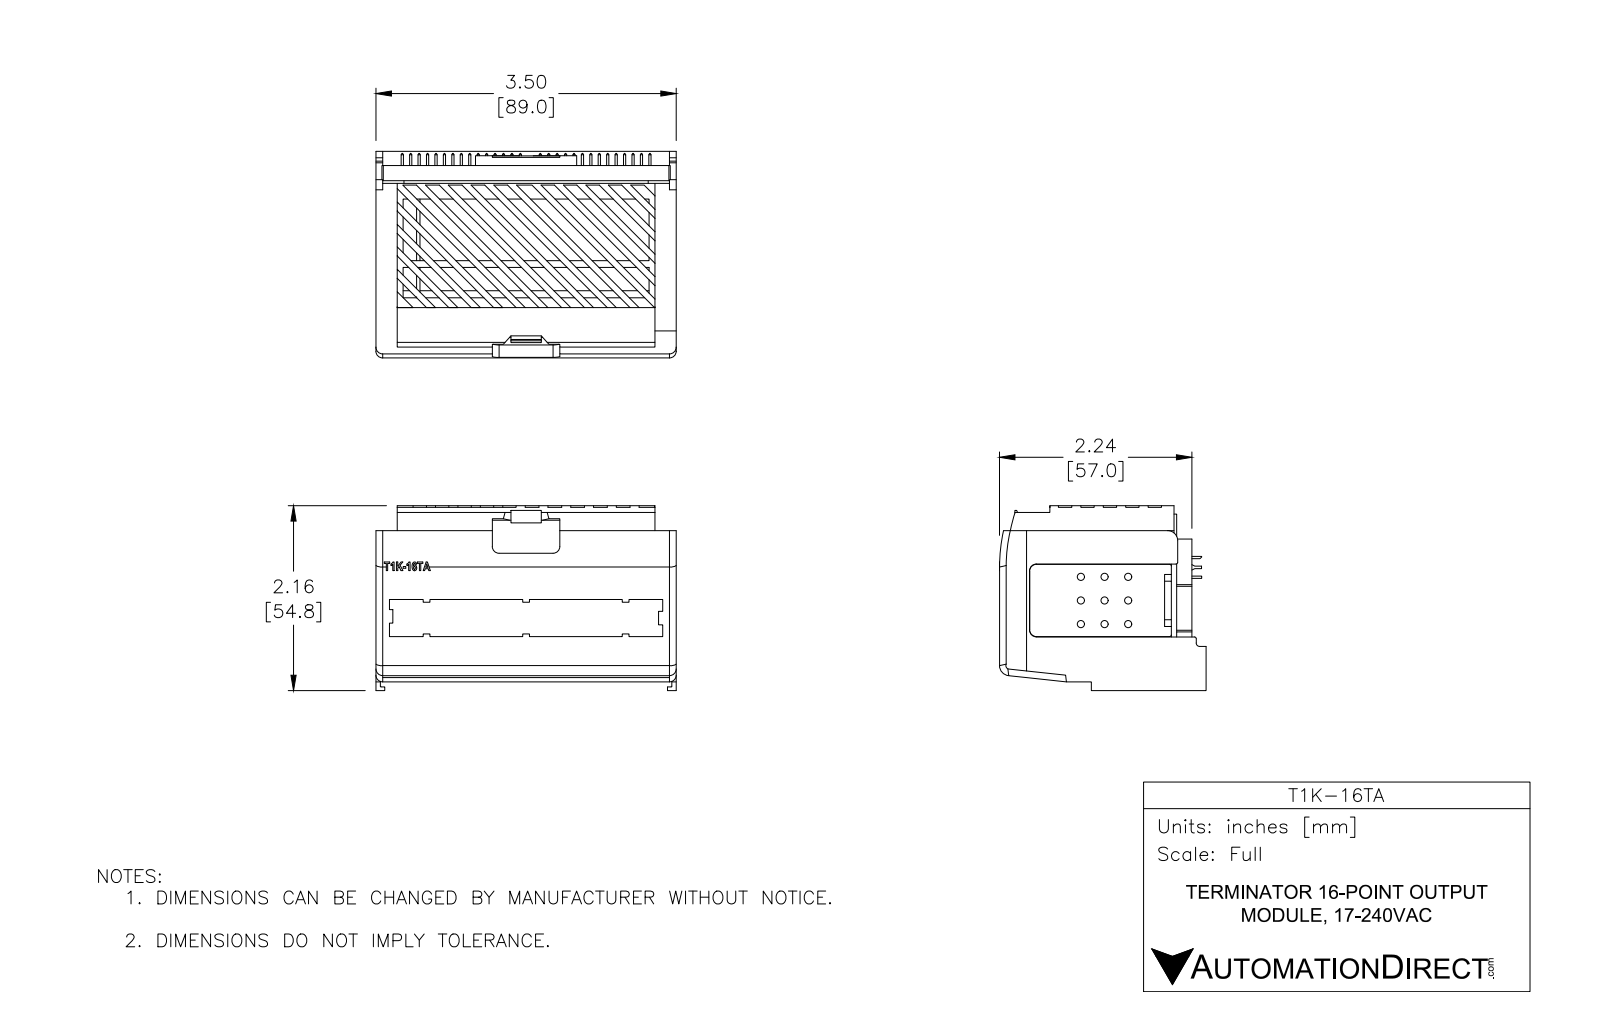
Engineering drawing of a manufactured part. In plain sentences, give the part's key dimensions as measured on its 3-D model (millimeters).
The part is named "T1K-16TA". Its 3-D file was written by "SolidWorks 2013 (AUTOMOTIVE_DESIGN)". It is 1 solid with 630 faces: 439 planar, 181 cylindrical and 10 other. Overall it measures 88.7 by 65.1 by 61.36 millimeters. Its volume is 45 450 cubic millimeters and its surface area 54 522 square millimeters. Round holes: 16 of diameter 3. Round bosses or shafts: 56 of diameter 0.7. Partial cylindrical surfaces (rounded edges, fillets, slot ends): 18 of radius 3.5, 5 of radius 1, 3 of radius 0.25, 3 of radius 0.55, 2 of radius 1.5, 1 of radius 8, 1 of radius 10, 1 of radius 18. The main face-to-face distances are 2, 86.7, 55.35, 0.5, 59.8, 88.7, 1.5, 55.26, 53.35, 84.7. The hole center spacings are 5.15, 10.3, 15.45, 20.6, 25.75, 30.9, 36.05, 41.2.
